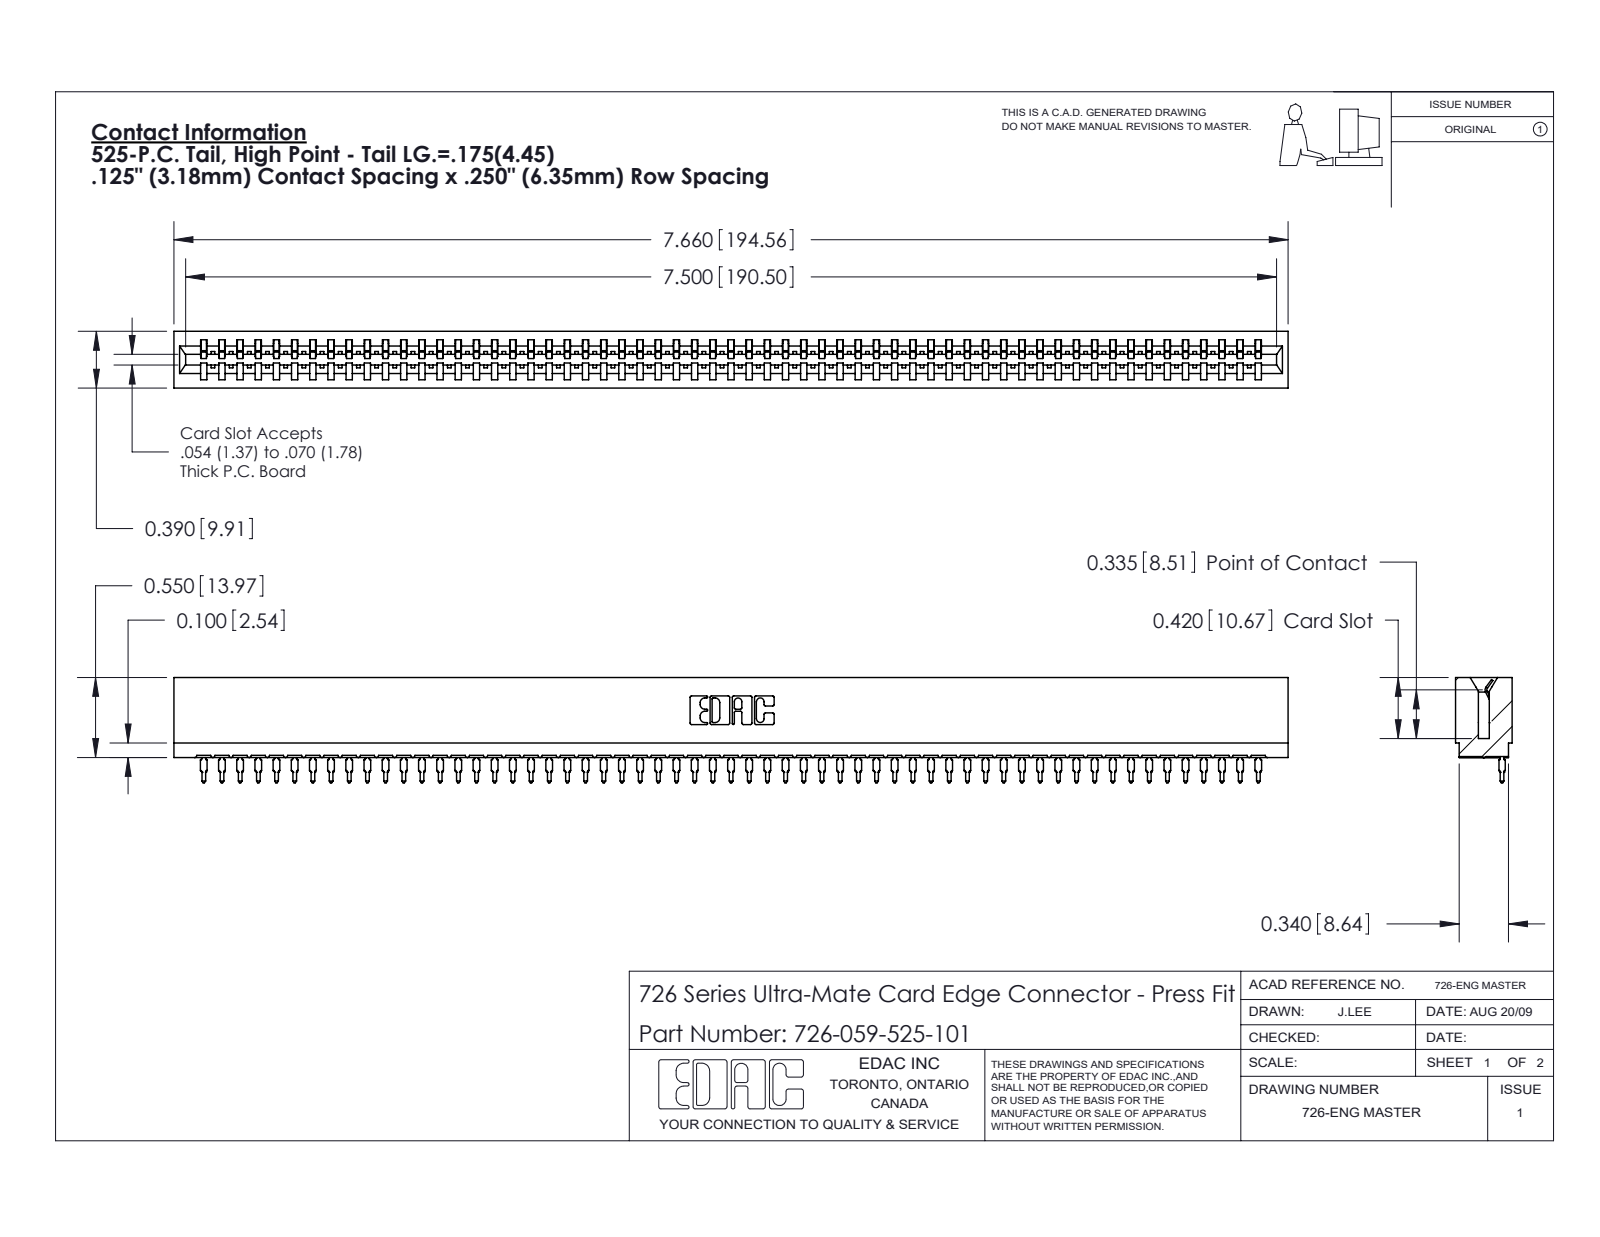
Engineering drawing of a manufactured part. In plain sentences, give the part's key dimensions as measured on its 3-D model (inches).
The part is named "726 Part_.515 Slot Depth - 01; 746-292-001_525; 726-059-525-101". Its 3-D file was written by "SolidWorks 2020 (CONFIG_CONTROL_DESIGN)". It is 60 solids with 6469 faces: 3772 planar, 1163 cylindrical and 1534 other. Overall it measures 7.66 by 0.724 by 0.39 inches. Its volume is 1.05 cubic inches and its surface area 40.65 square inches. Partial cylindrical surfaces (rounded edges, fillets, slot ends): 118 of radius 0.021, 60 of radius 0.015, 22 of radius 0.01, 6 of radius 0.007, 6 of radius 0.031, 4 of radius 0.005, 4 of radius 0.011, 3 of radius 0.026. The main face-to-face distances are 0.057, 0.333, 0.39, 0.025, 0.307, 0.25, 0.275, 0.365, 0.032, 0.174.
